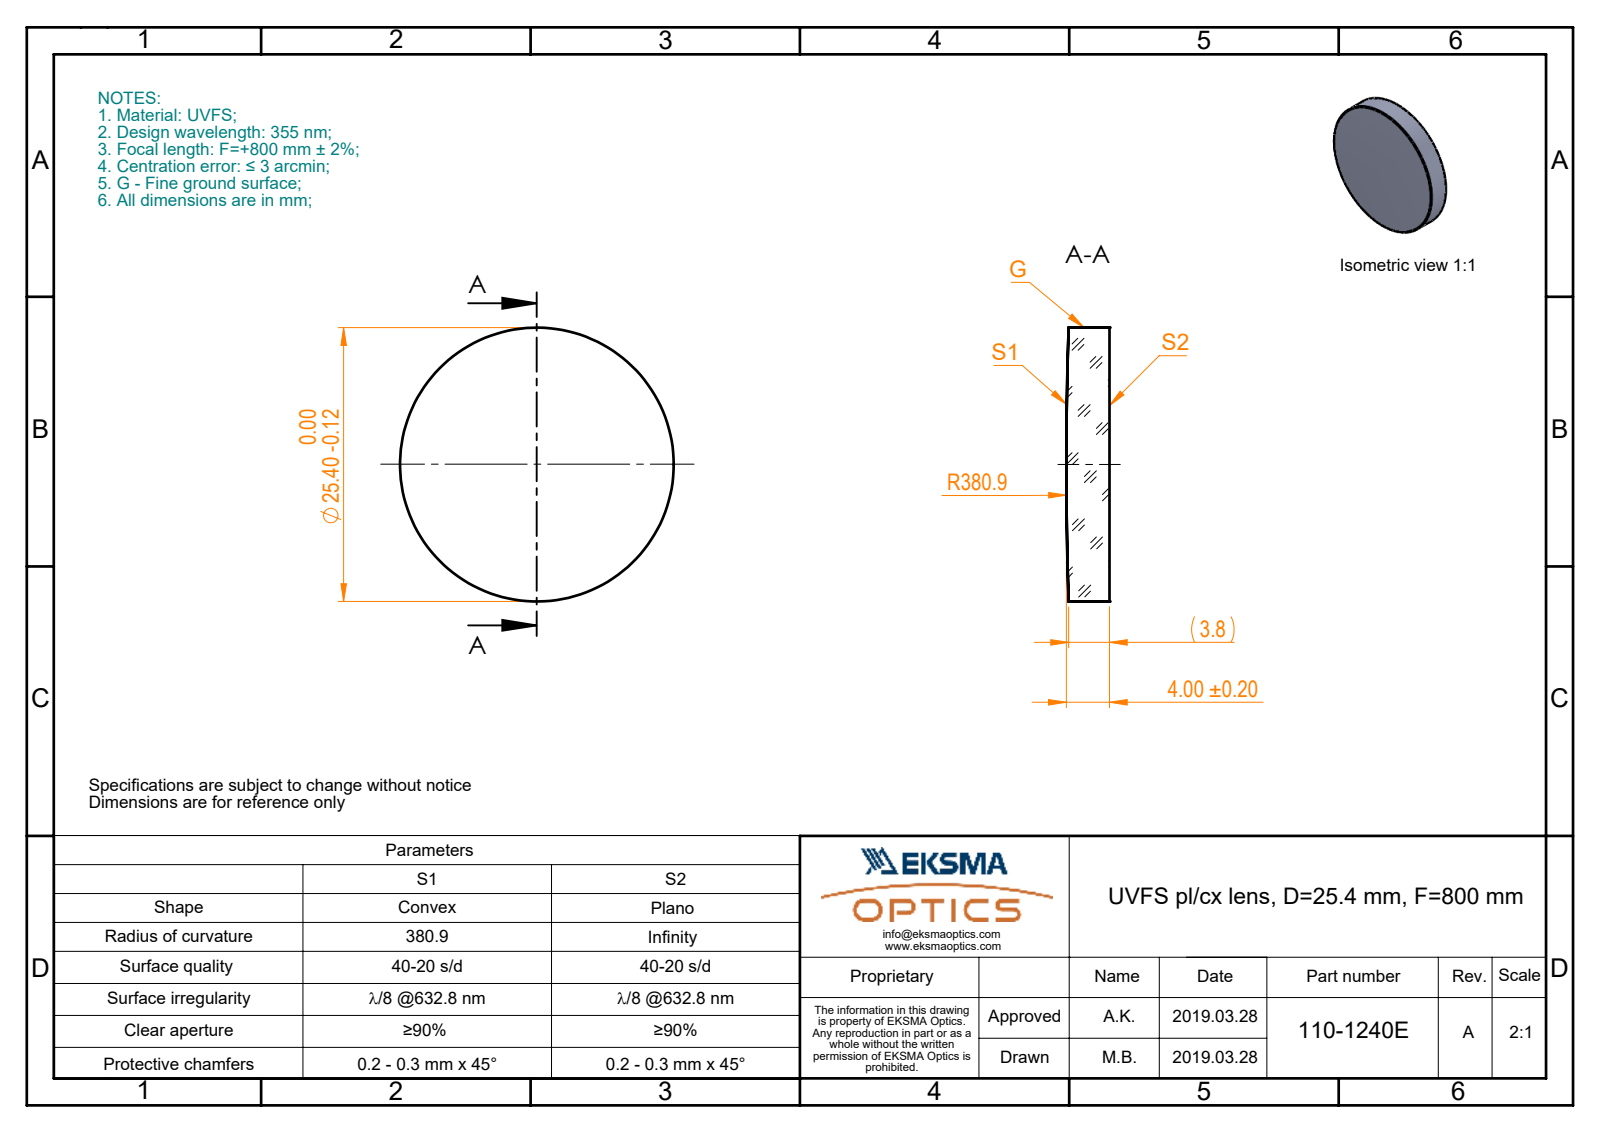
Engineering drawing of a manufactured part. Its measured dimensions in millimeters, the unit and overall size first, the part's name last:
Units: millimetres
Overall size (bounding box): 25.4 × 25.4 × 4
Round bosses / shafts (diameter × count): ⌀25.4 ×1
Volume: 1 973 mm³ · Surface area: 1 316 mm²
Bodies: 1 solid, 5 faces (1 planar, 2 cylindrical, 2 other)
Part name (STEP PRODUCT): 110-1240E UVFS pl-cx 25.4 F800
STEP written by: SolidWorks 2017 (CONFIG_CONTROL_DESIGN)
